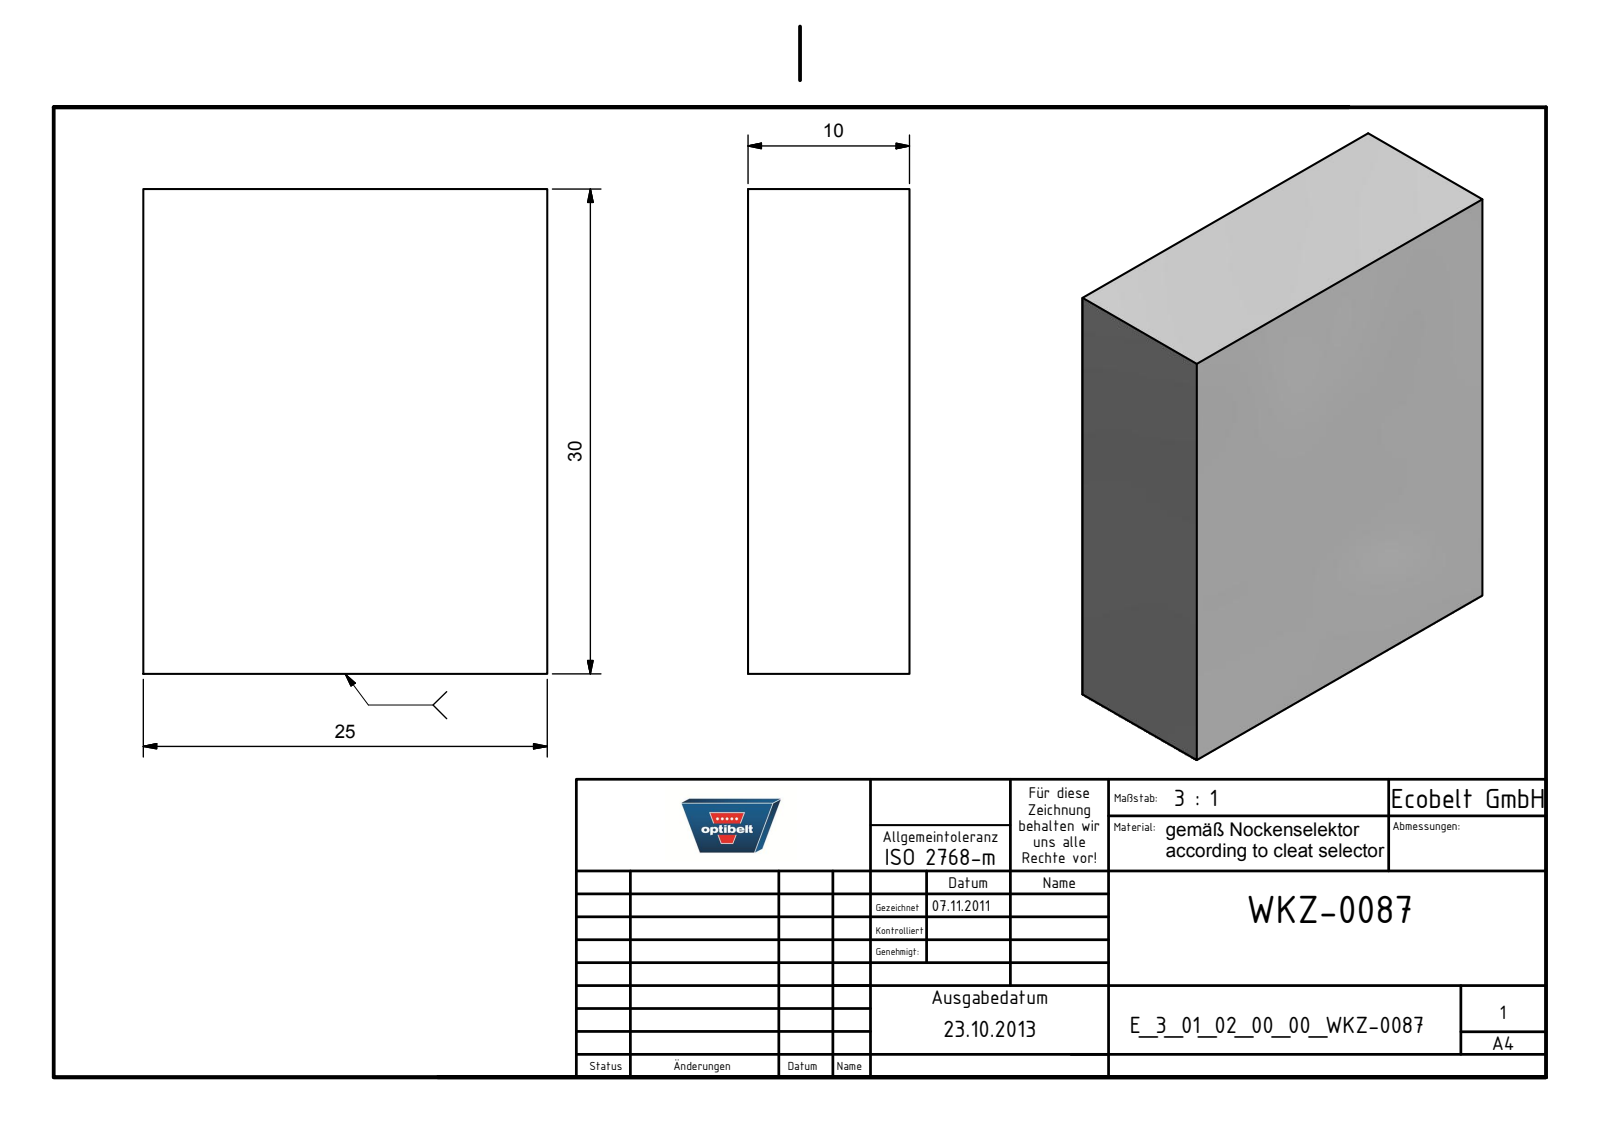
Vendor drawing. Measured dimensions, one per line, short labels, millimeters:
name: E_3_01_02_00_00_WKZ-0087
written by: Autodesk Inventor 2021 (AUTOMOTIVE_DESIGN)
unit: mm
bodies: 1 solid, 6 faces (6 planar, 0 cylindrical, 0 other)
size: 30 × 25 × 10
volume: 7 500 mm³; area: 2 600 mm²
face distances: 10, 25, 30
